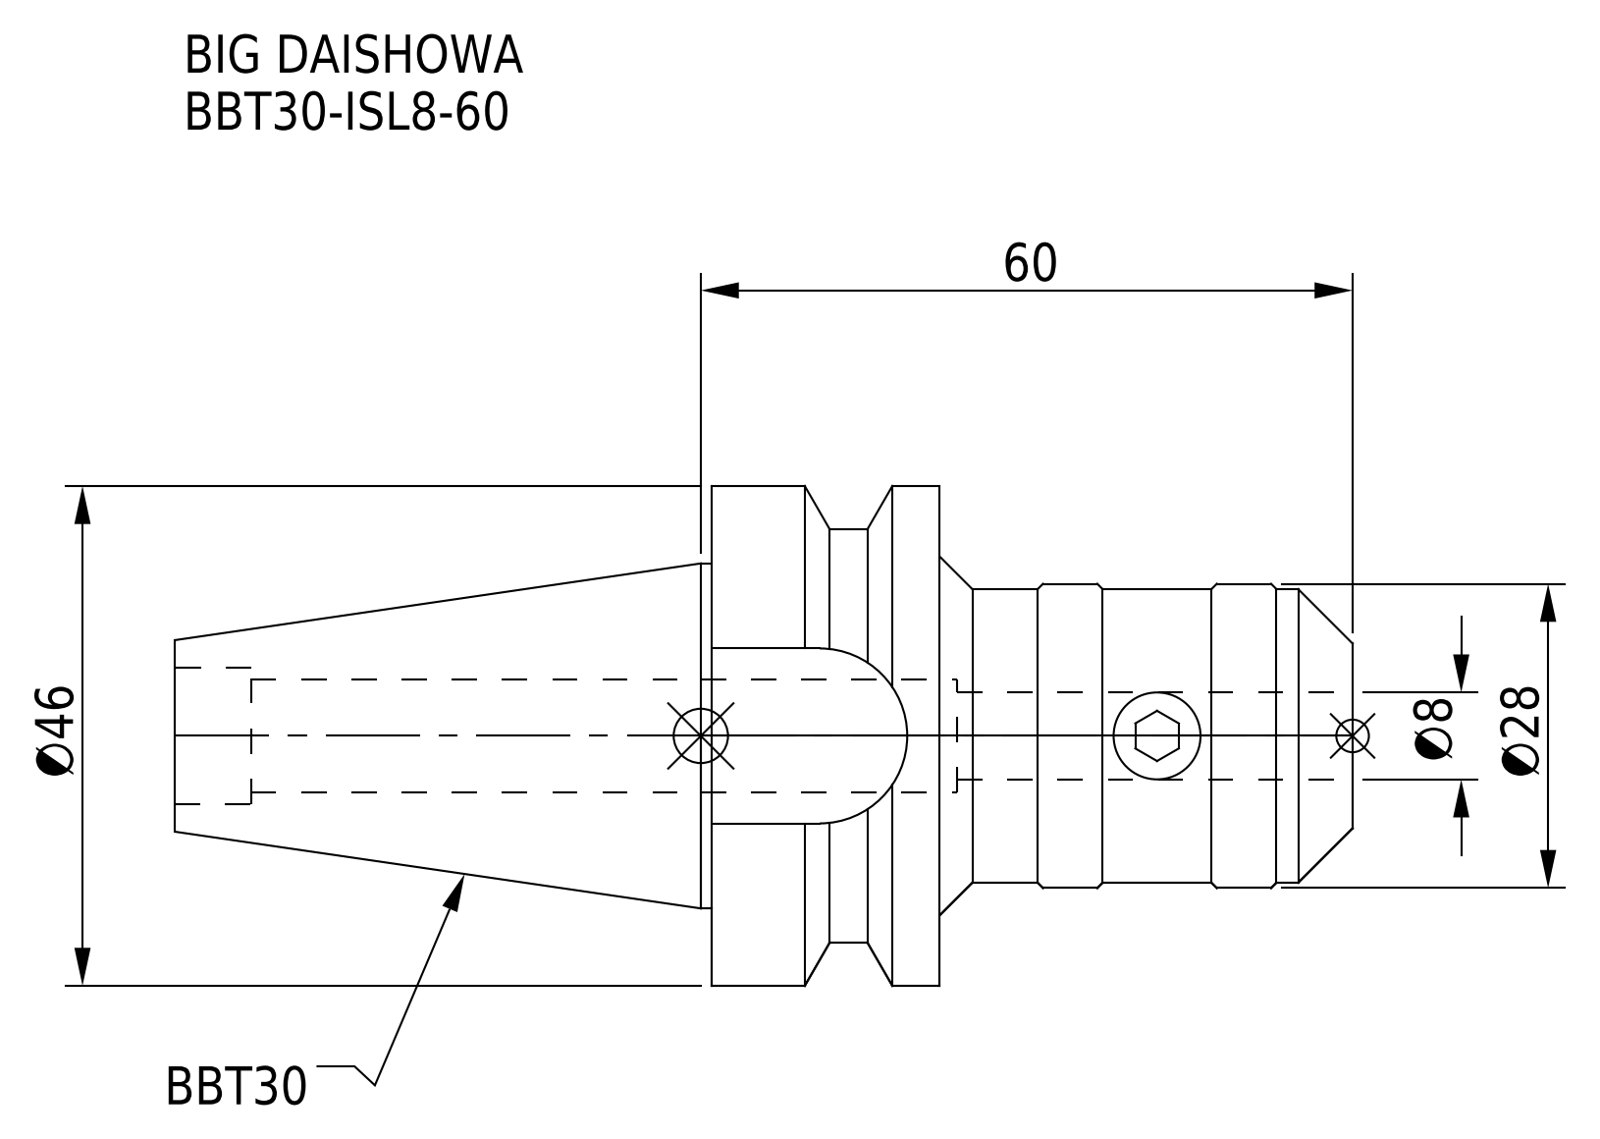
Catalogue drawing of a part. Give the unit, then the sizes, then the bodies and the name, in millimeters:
Units: millimetres
Overall size (bounding box): 108.4 × 46 × 46
Round holes (diameter × count): ⌀8 ×1, ⌀10.4 ×1, ⌀12.5 ×1
Round bosses / shafts (diameter × count): ⌀46 ×1, ⌀31.75 ×1, ⌀28 ×1, ⌀27 ×1
Partial cylindrical surfaces — rounded edges, fillets, slot ends (radius × count): R8.05 ×1, R19 ×1
Main face-to-face distances: 21, 32.6, 38, 59, 108.4, 70.4, 49.4, 16.1, 101.4, 63.4
Volume: 67 332 mm³ · Surface area: 16 354 mm²
Bodies: 1 solid, 58 faces (12 planar, 28 cylindrical, 18 other)
Part name (STEP PRODUCT): BBT30-ISL8-60
STEP written by: CREO PARAMETRIC BY PTC INC, 2016380 (AUTOMOTIVE_DESIGN)
